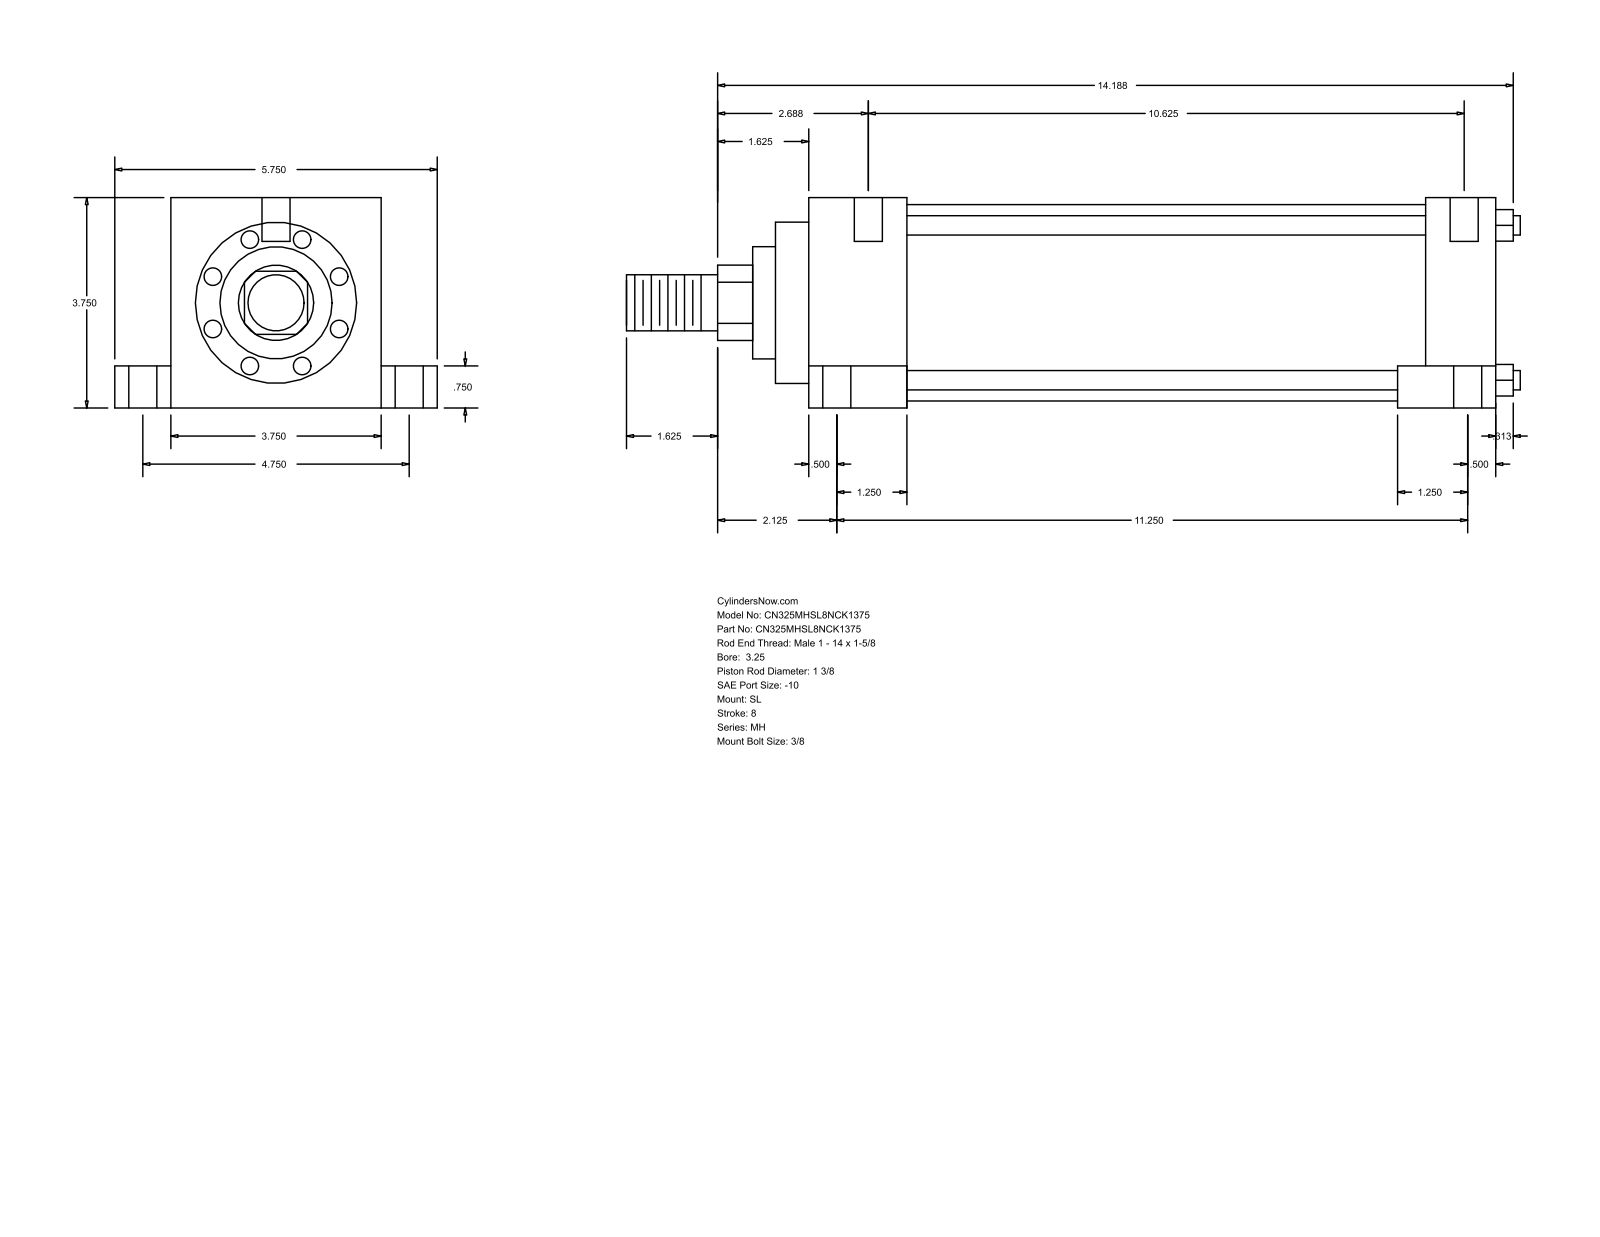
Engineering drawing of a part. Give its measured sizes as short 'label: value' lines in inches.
name: MH_SL__0325_1.375
written by: GSSL Pune (CONFIG_CONTROL_DESIGN)
unit: in
bodies: 0 solids, 110 faces (77 planar, 33 cylindrical, 0 other)
size: 15.937 × 5.75 × 3.75
holes: 6× ⌀0.5, 4× ⌀0.219, 4× ⌀0.75
bosses: 4× ⌀0.345, 1× ⌀3.5, 1× ⌀2.875, 1× ⌀2, 1× ⌀1.375, 1× ⌀1
rounds: 1× R0.672
face distances: 3.75, 12.25, 1.75, 10.5, 1, 4.75, 0.75, 3, 11, 9.25
hole spacings: 2.376, 2.378, 2.427, 2.441, 4.75, 10.875, 10.948, 11.01
